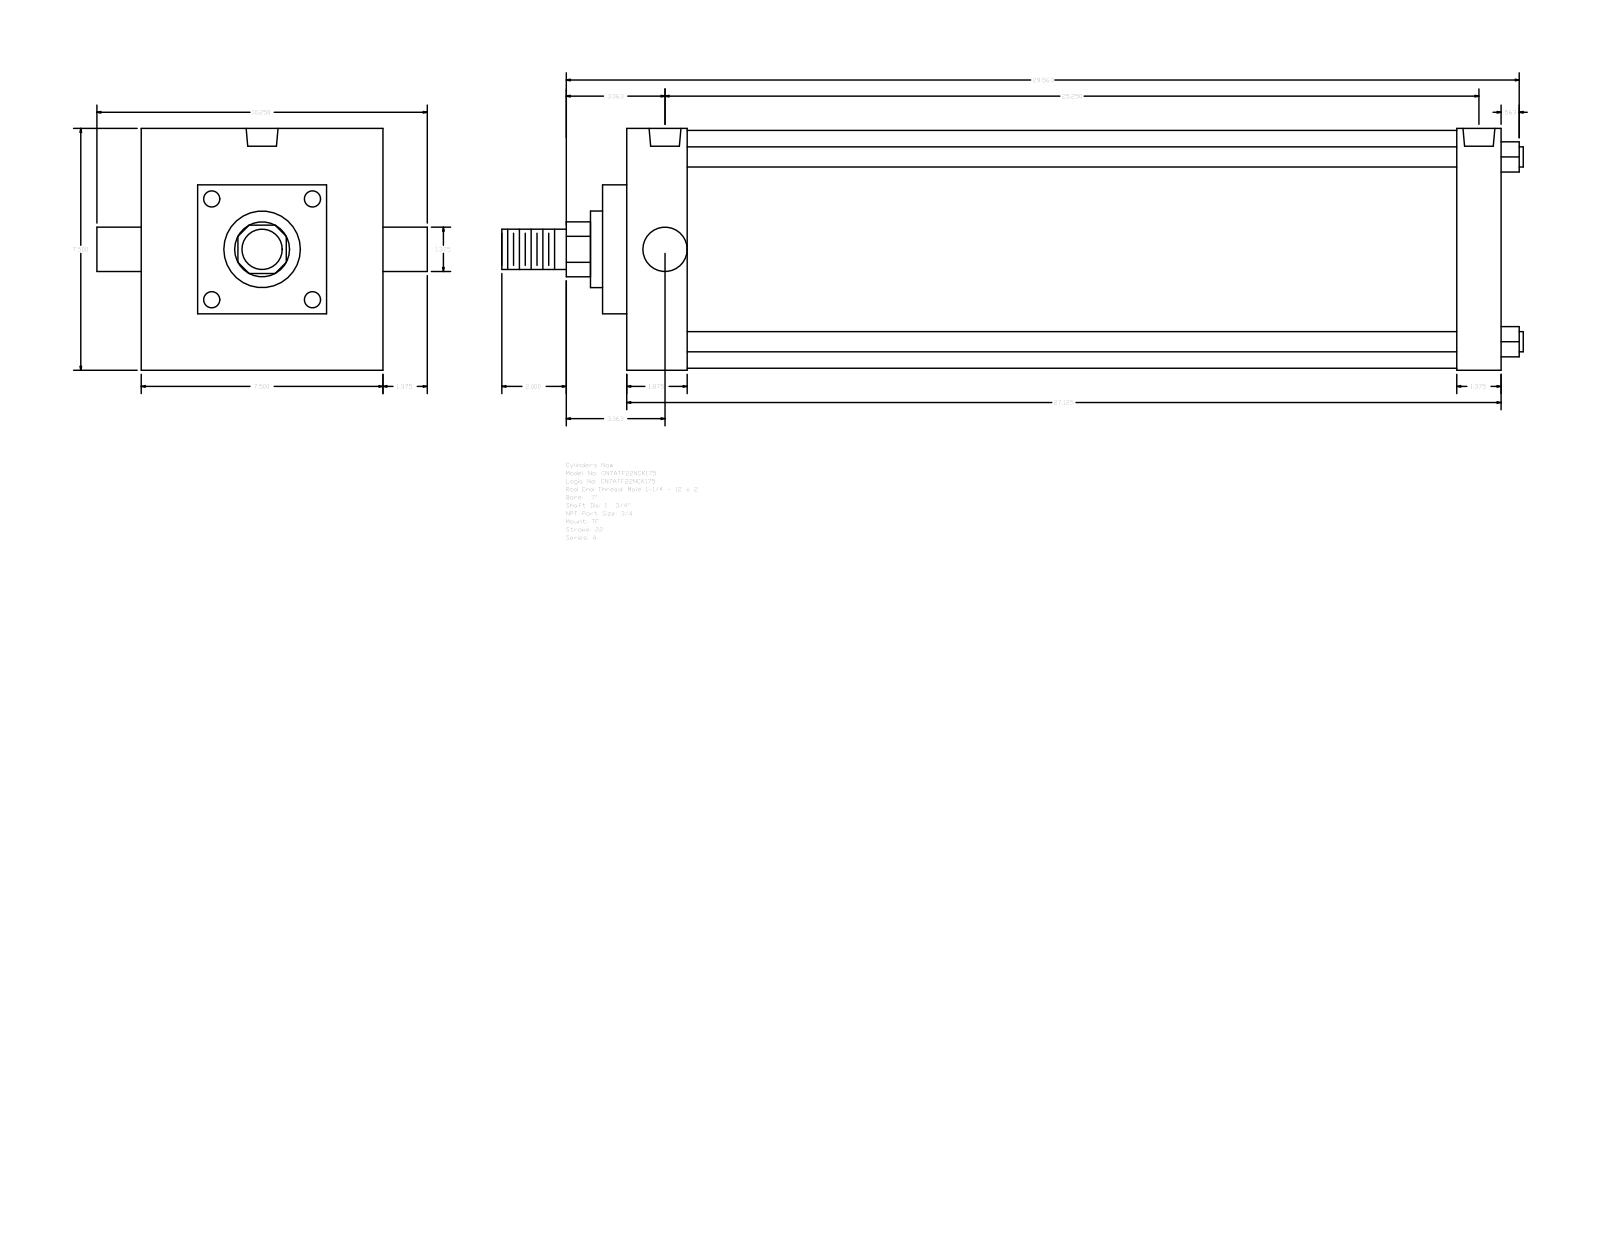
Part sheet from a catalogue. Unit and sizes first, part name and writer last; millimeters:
Units: millimetres
Overall size (bounding box): 804.86 × 260.35 × 190.5
Round holes (diameter × count): ⌀15.08 ×3, ⌀25.12 ×2
Round bosses / shafts (diameter × count): ⌀15.88 ×4, ⌀187.32 ×1, ⌀60.33 ×1, ⌀44.45 ×1, ⌀34.92 ×1, ⌀31.75 ×1
Partial cylindrical surfaces — rounded edges, fillets, slot ends (radius × count): R21.63 ×1
Main face-to-face distances: 190.5, 688.98, 34.93, 146.05, 19.05, 47.63, 641.35, 654.05, 606.42, 44.45
Hole centre spacings: 5.56, 635.79, 630.23, 641.35
Bodies: 0 solids, 89 faces (65 planar, 24 cylindrical, 0 other)
Part name (STEP PRODUCT): A_TF__0700_1.75
STEP written by: GSSL Pune (CONFIG_CONTROL_DESIGN)
